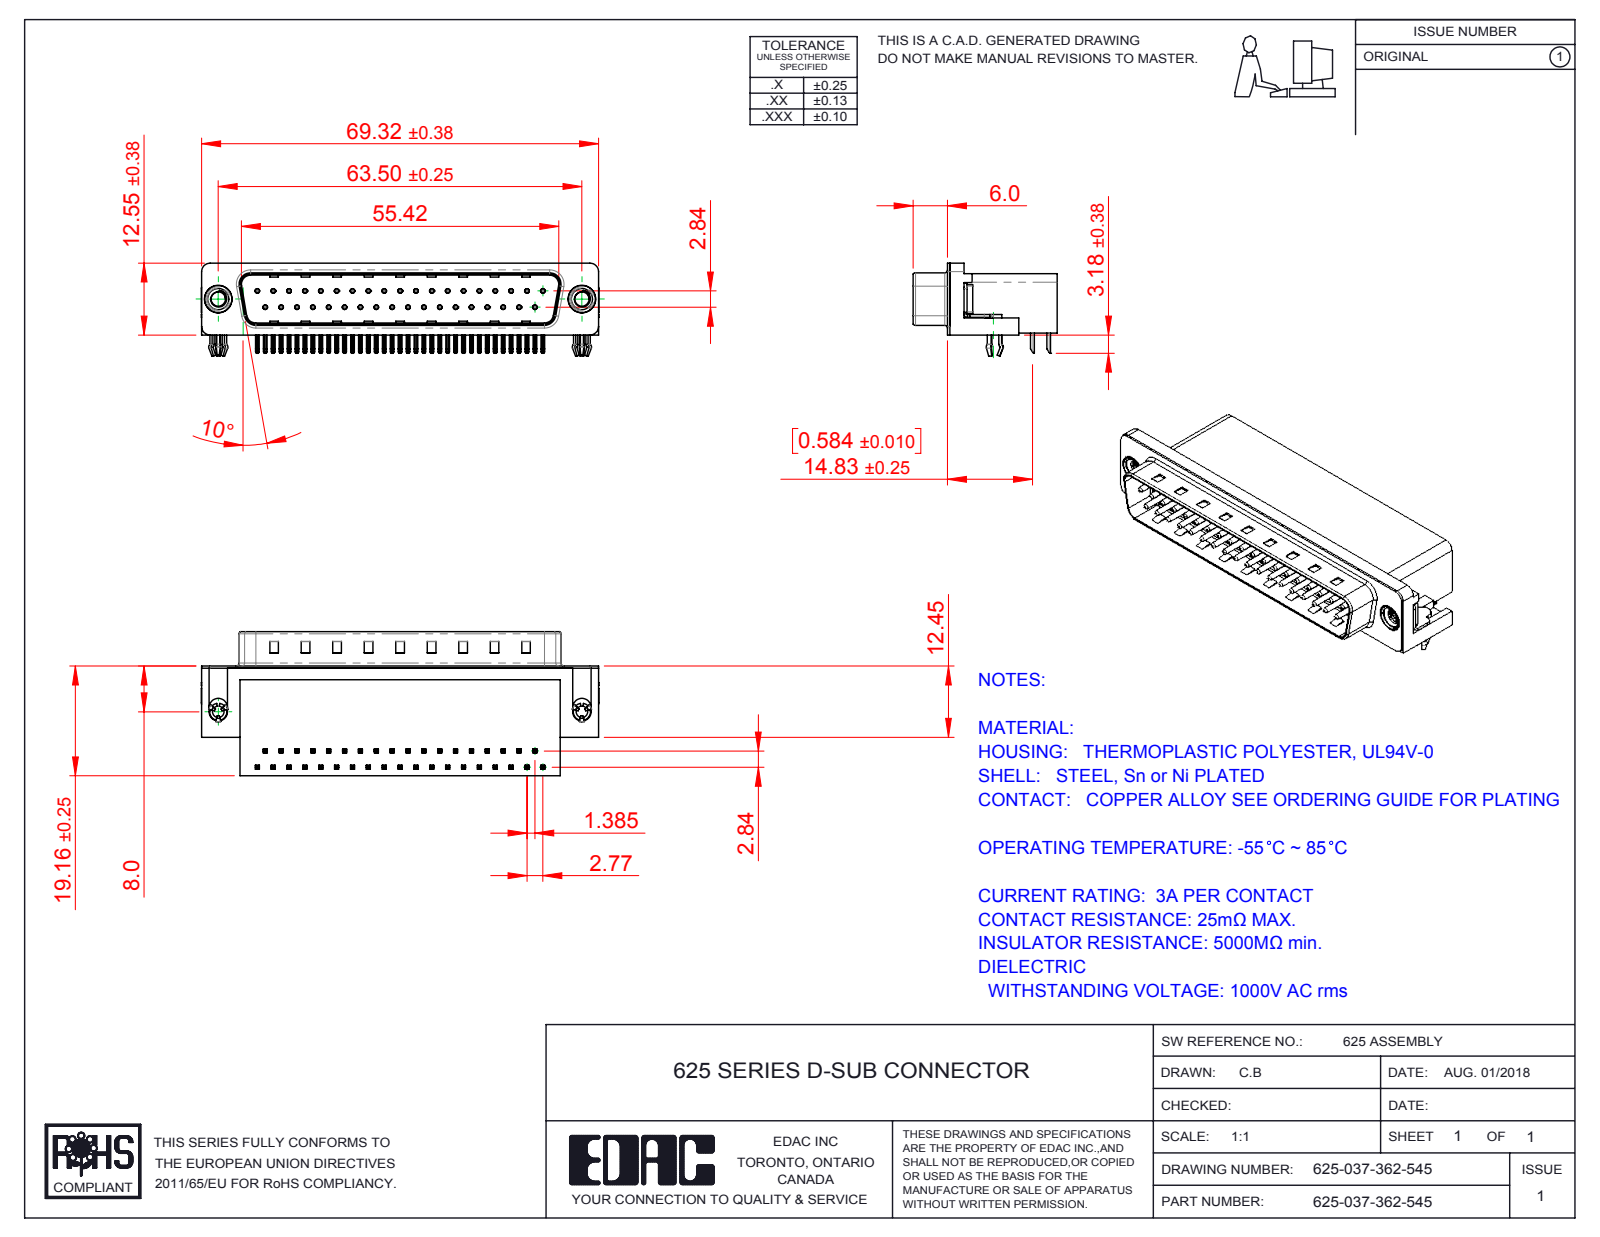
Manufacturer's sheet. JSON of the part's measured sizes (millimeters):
{"part_name": "625 Contact Bottom; 625 M3 Threaded Rivet; 625-037-362-545; 625 Housing_37 Socket (+3 more)", "step_written_by": "SolidWorks 2016 (CONFIG_CONTROL_DESIGN)", "units": "millimeters", "bodies": {"solids": 43, "faces": 3305, "planar": 2051, "cylindrical": 927, "other": 327}, "overall_size": [69.4, 25.16, 16.25], "volume_mm3": 12604, "surface_area_mm2": 11818, "round_holes": [[0.35, 37], [0.8, 37], [2, 2], [2.5, 2], [4, 2], [4.8, 2], [5, 2]], "round_bosses_or_shafts": [[0.75, 37], [4.9, 2], [4.75, 2], [3.9, 2], [3, 2]], "partial_cylinders_radius": [[0.25, 160], [0.12, 74], [1, 16], [0.5, 9], [1.6, 8], [1.5, 7], [0.9, 4], [2, 4]], "face_to_face_distances": [10.34, 0.4, 18.76, 8.76, 19.16, 2.84, 2.09, 10.1, 1.74, 8.36], "hole_center_spacings": [3.16, 2.77, 5.54, 8.31, 11.08, 13.85, 19.39, 22.16]}
